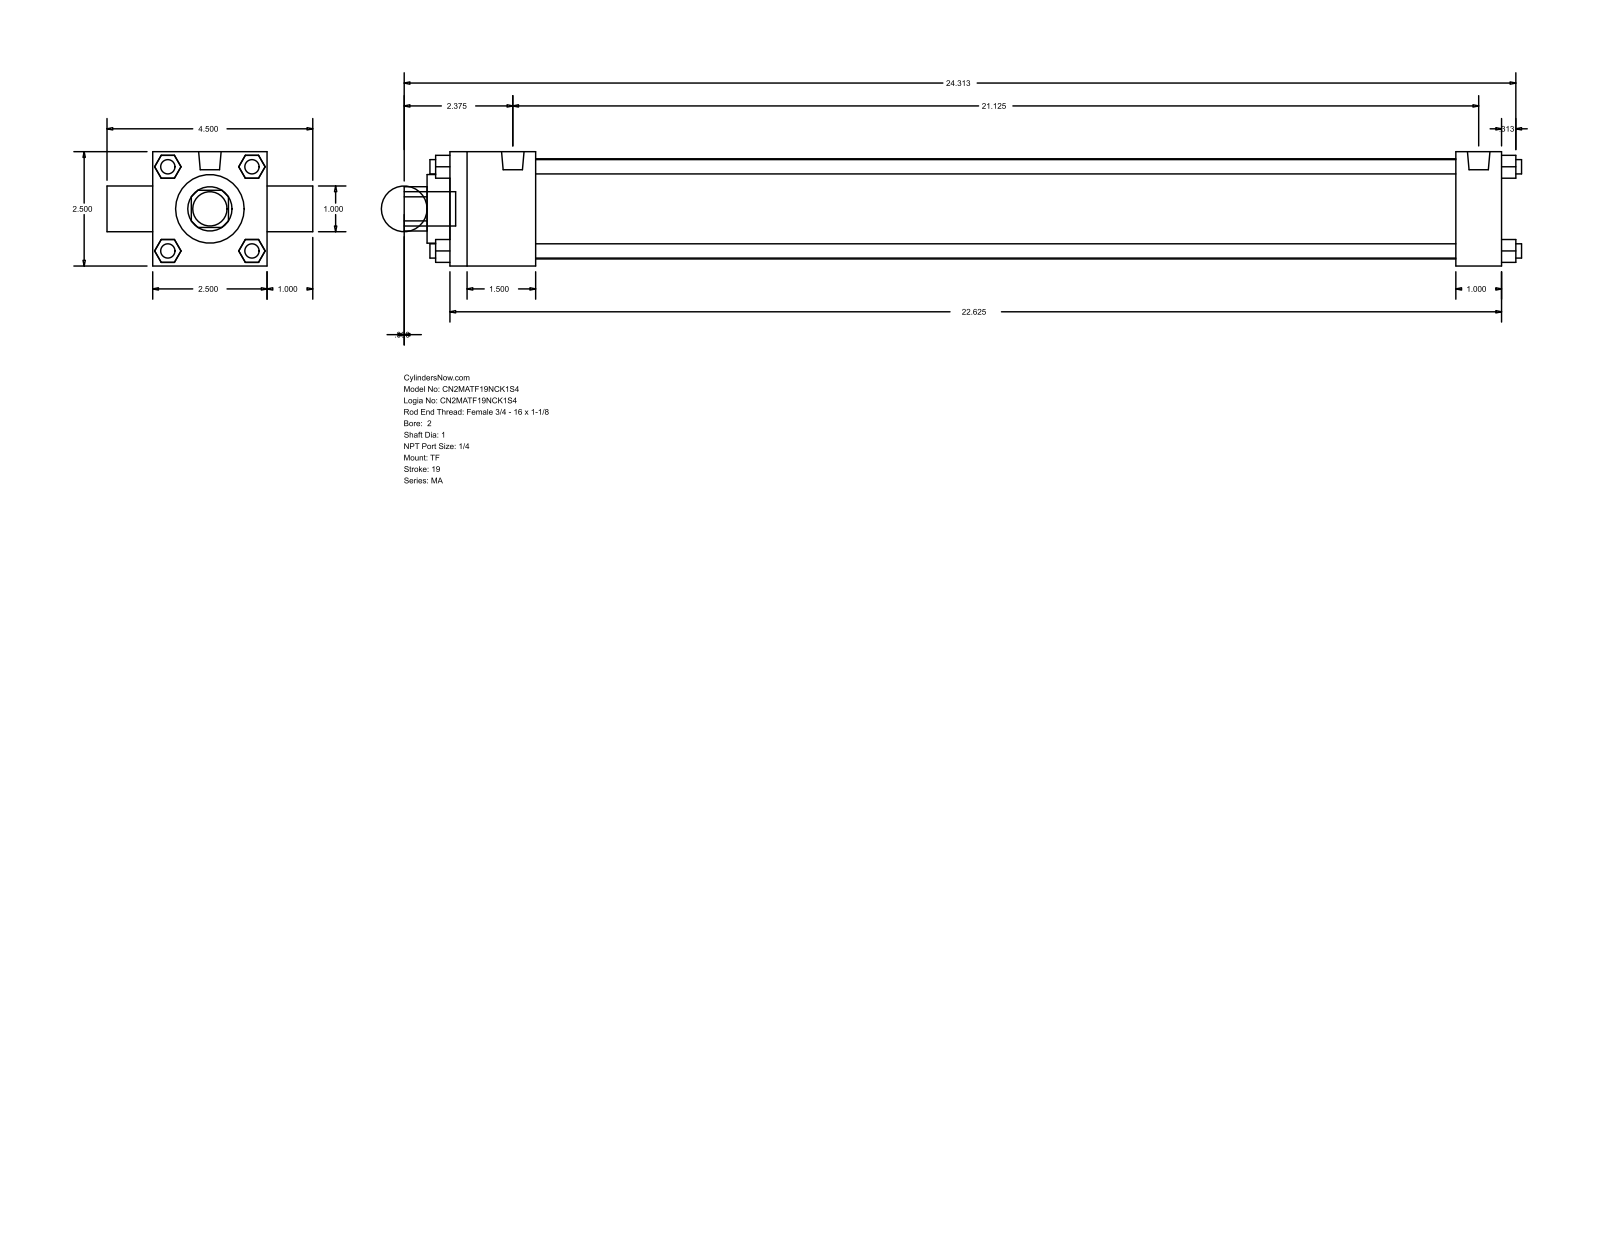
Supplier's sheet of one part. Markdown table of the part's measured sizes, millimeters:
| quantity | value |
| --- | --- |
| part name | MA_TF__0200_1 |
| STEP written by | GSSL Pune (CONFIG_CONTROL_DESIGN) |
| units | millimeters |
| bodies | 0 solids, 120 faces (92 planar, 28 cylindrical, 0 other) |
| overall size | 620.71 × 114.3 × 63.5 |
| round holes (diameter × count) | 25.4 × 2, 38.1 × 1, 55.63 × 1 |
| round bosses / shafts (diameter × count) | 7.94 × 7, 12.49 × 2, 19.05 × 1 |
| partial cylindrical surfaces (radius × count) | 12.29 × 1 |
| main face-to-face distances | 63.5, 25.4, 584.2, 12.7, 47.63, 558.8, 511.17, 536.57, 88.9, 23.37 |
